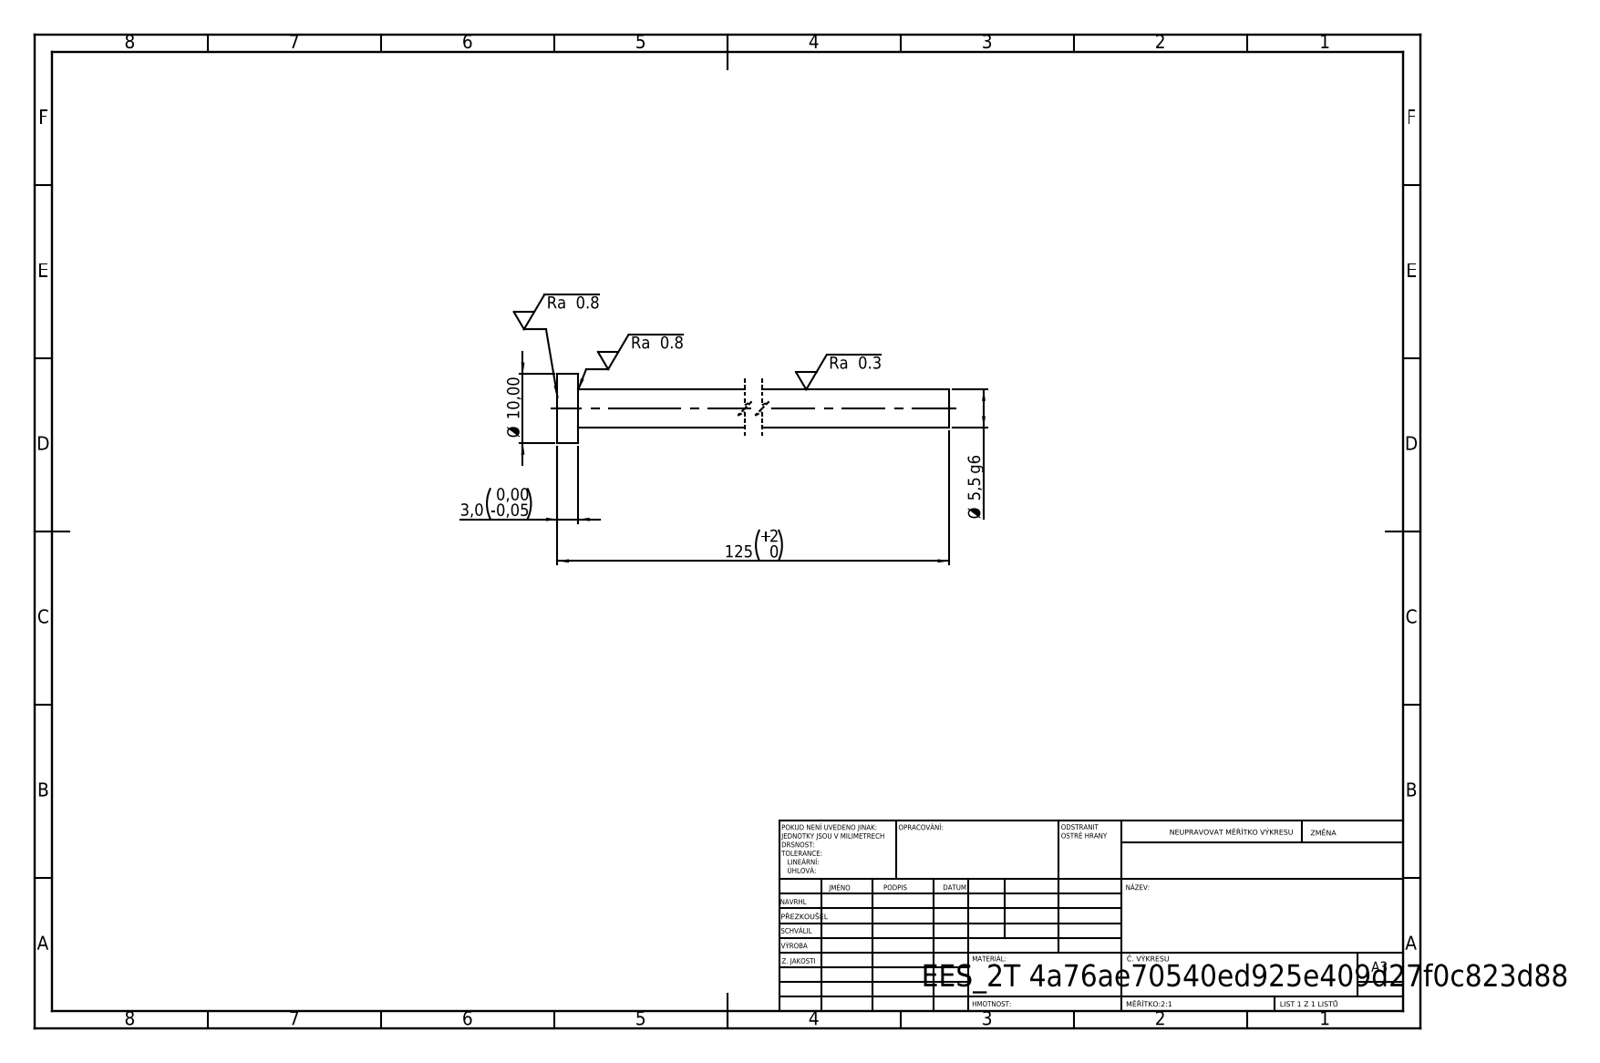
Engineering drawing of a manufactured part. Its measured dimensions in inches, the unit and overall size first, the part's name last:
Units: inches
Overall size (bounding box): 4.921 × 0.394 × 0.394
Round bosses / shafts (diameter × count): ⌀0.394 ×1, ⌀0.217 ×1
Main face-to-face distances: 0.118, 4.921, 4.803
Volume: 0.191 in³ · Surface area: 3.656 in²
Bodies: 1 solid, 7 faces (3 planar, 4 cylindrical, 0 other)
STEP written by: SolidWorks 2019 (CONFIG_CONTROL_DESIGN)
